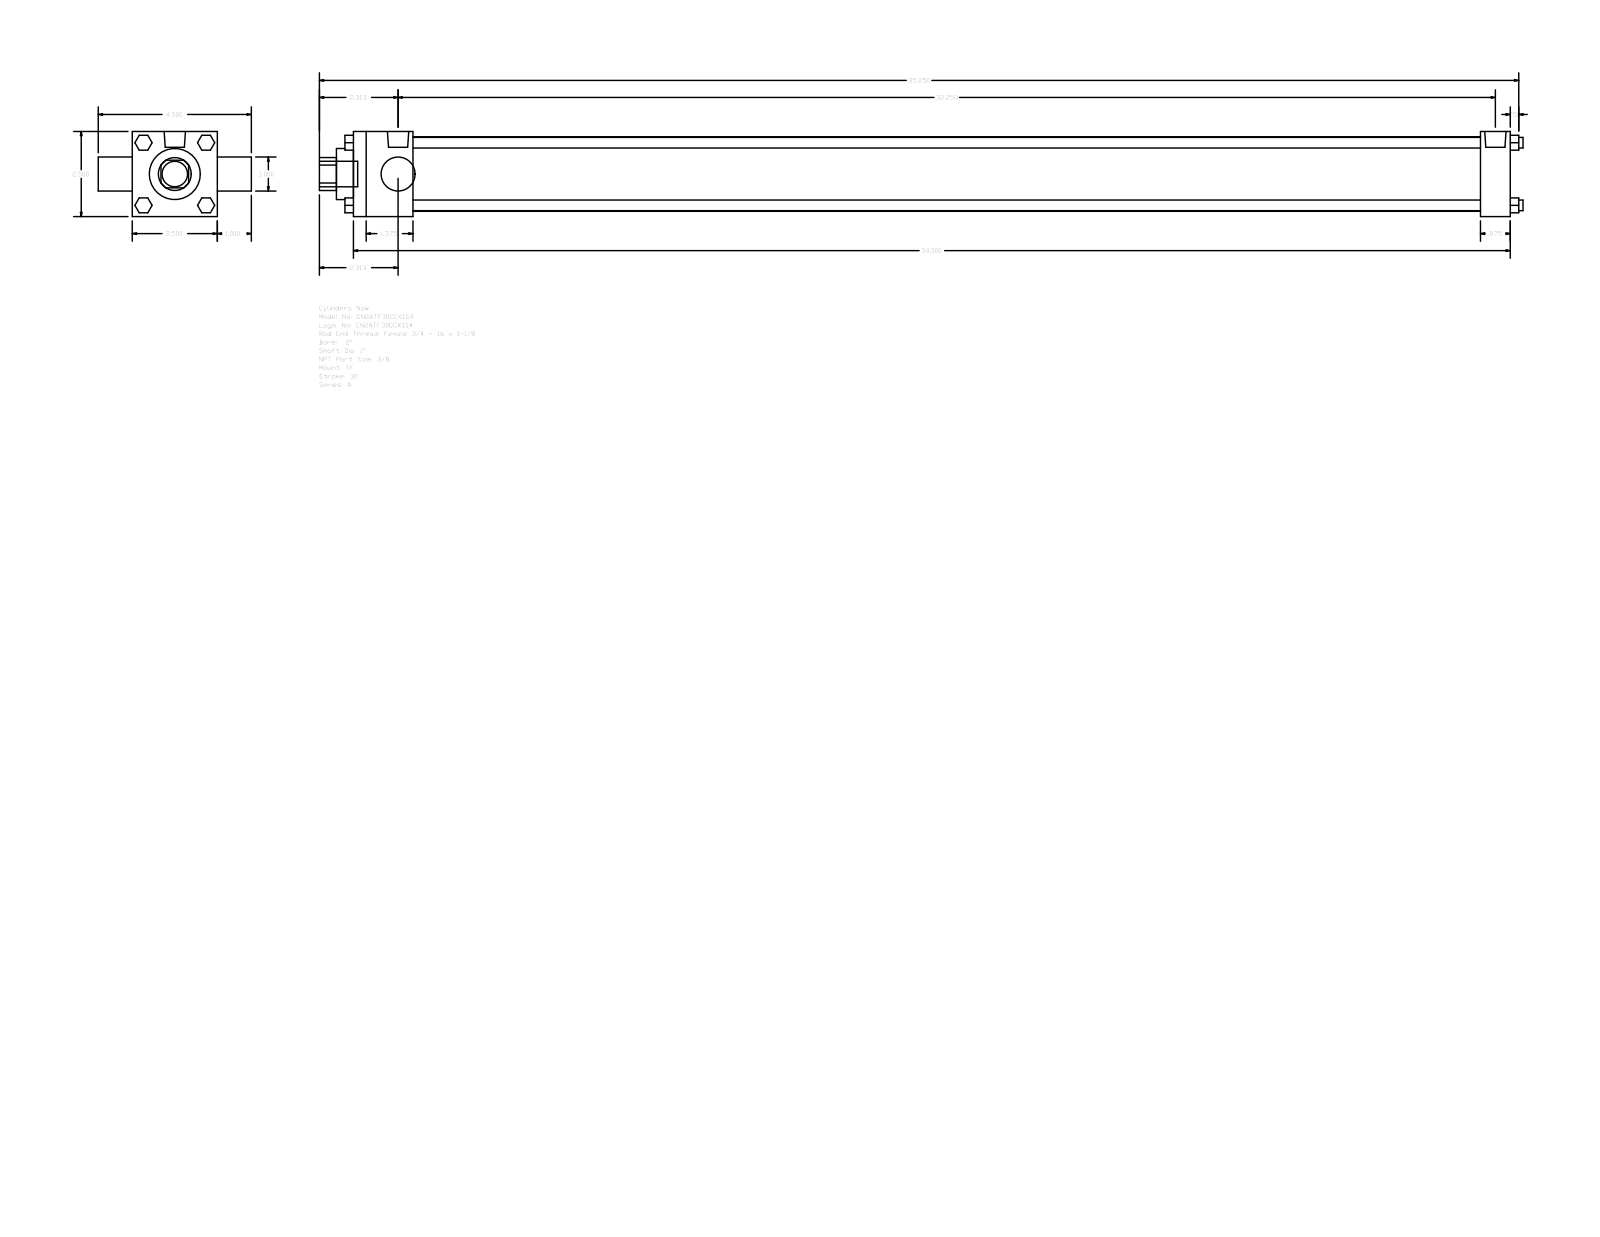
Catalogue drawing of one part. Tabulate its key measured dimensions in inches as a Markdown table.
| quantity | value |
| --- | --- |
| part name | A_TF__0200_1 |
| STEP written by | GSSL Pune (CONFIG_CONTROL_DESIGN) |
| units | inches |
| bodies | 0 solids, 120 faces (92 planar, 28 cylindrical, 0 other) |
| overall size | 35.375 × 4.5 × 2.5 |
| round holes (diameter × count) | 1 × 2, 1.5 × 1, 2.19 × 1 |
| round bosses / shafts (diameter × count) | 0.313 × 4, 0.219 × 3, 0.627 × 2, 0.75 × 1 |
| partial cylindrical surfaces (radius × count) | 0.484 × 1 |
| main face-to-face distances | 2.5, 34, 1.75, 33.125, 31.375, 32.25, 0.875, 1, 3.5, 34.5 |
